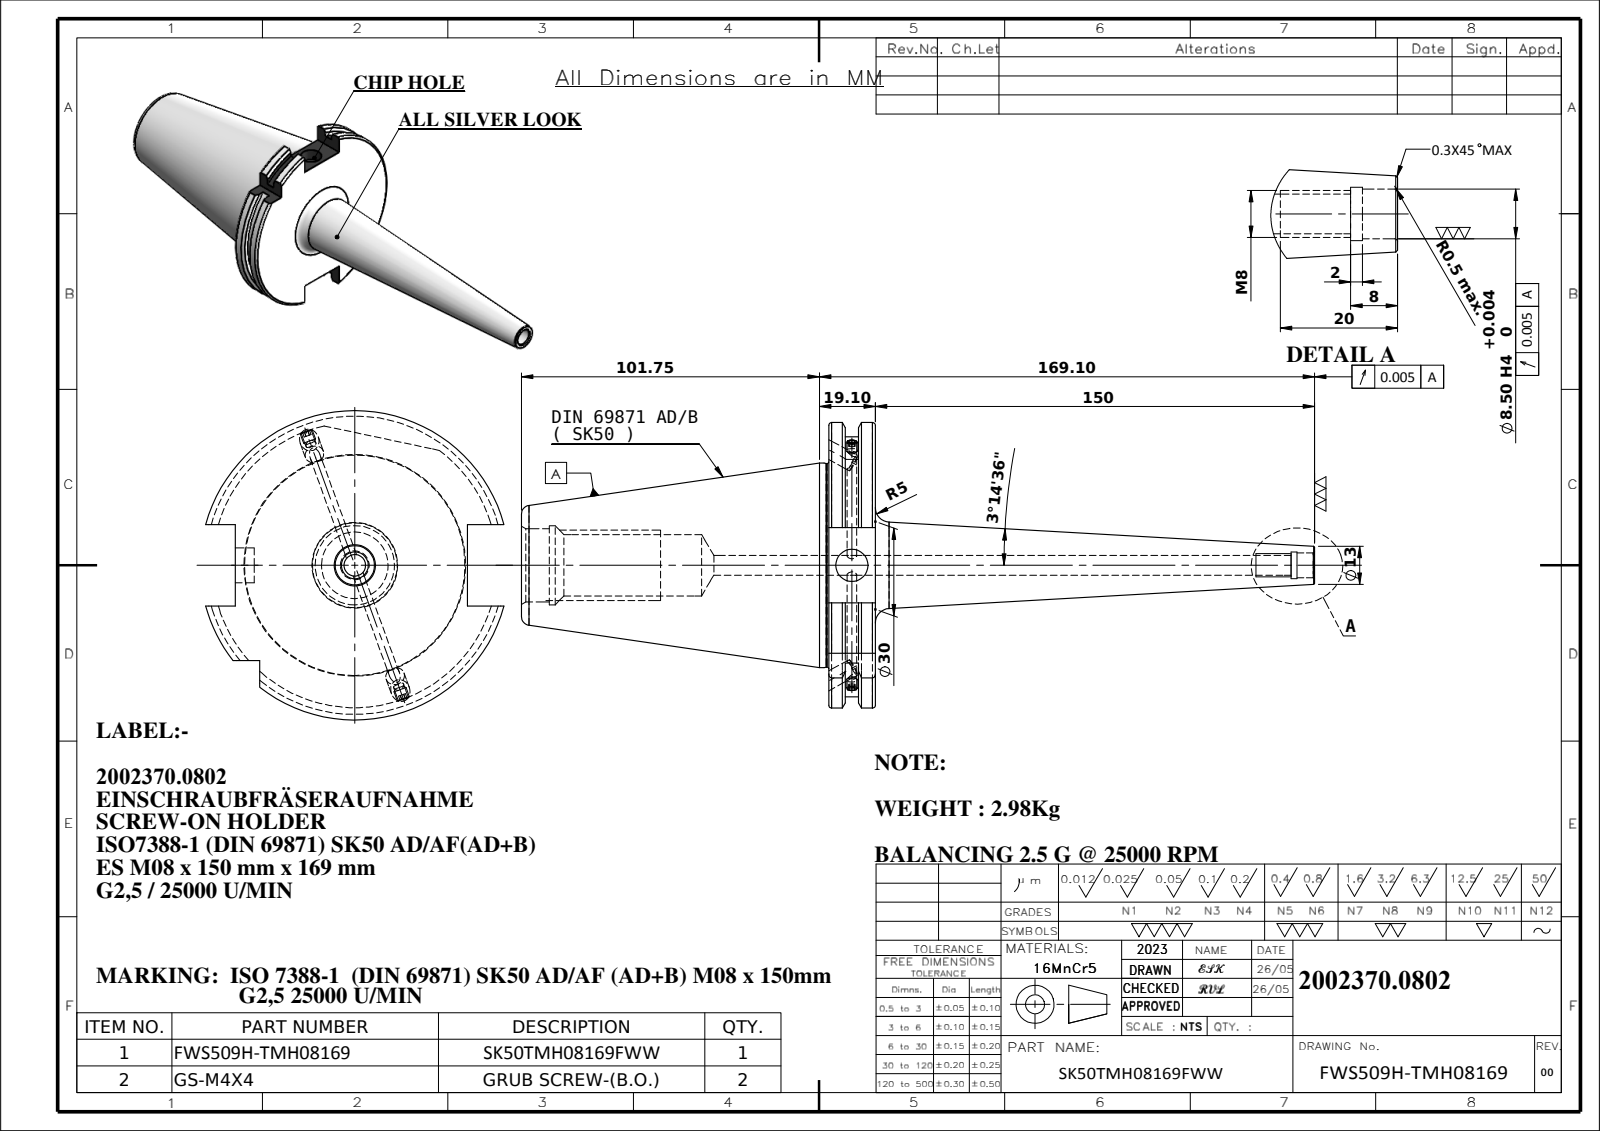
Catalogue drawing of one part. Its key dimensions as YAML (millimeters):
part_name: "SK50TMH08169FWW; M4X4_DIN 913 - M4 x 4-N; 91506-ES7M08150"
step_written_by: "SolidWorks 2018 (CONFIG_CONTROL_DESIGN)"
units: millimeters
bodies: {solids: 3, faces: 138, planar: 43, cylindrical: 47, other: 48}
overall_size: [270.85, 97.5, 94.05]
volume: 387653
surface_area: 55723
round_holes:
  - {diameter: 6, count: 2}
  - {diameter: 3.3, count: 1}
  - {diameter: 6.8, count: 1}
  - {diameter: 8.5, count: 1}
  - {diameter: 9.1, count: 1}
  - {diameter: 11, count: 1}
  - {diameter: 21, count: 1}
  - {diameter: 25, count: 1}
  - {diameter: 27, count: 1}
round_bosses_or_shafts:
  - {diameter: 4, count: 2}
  - {diameter: 69.85, count: 1}
  - {diameter: 69.45, count: 1}
partial_cylinders:
  - {radius: 44.9, count: 1}
  - {radius: 48.75, count: 1}
face_to_face_distances: [15.9, 5.66, 10.24, 10.14, 4.48, 5.76, 104.95, 110.61, 115.09, 120.85]
